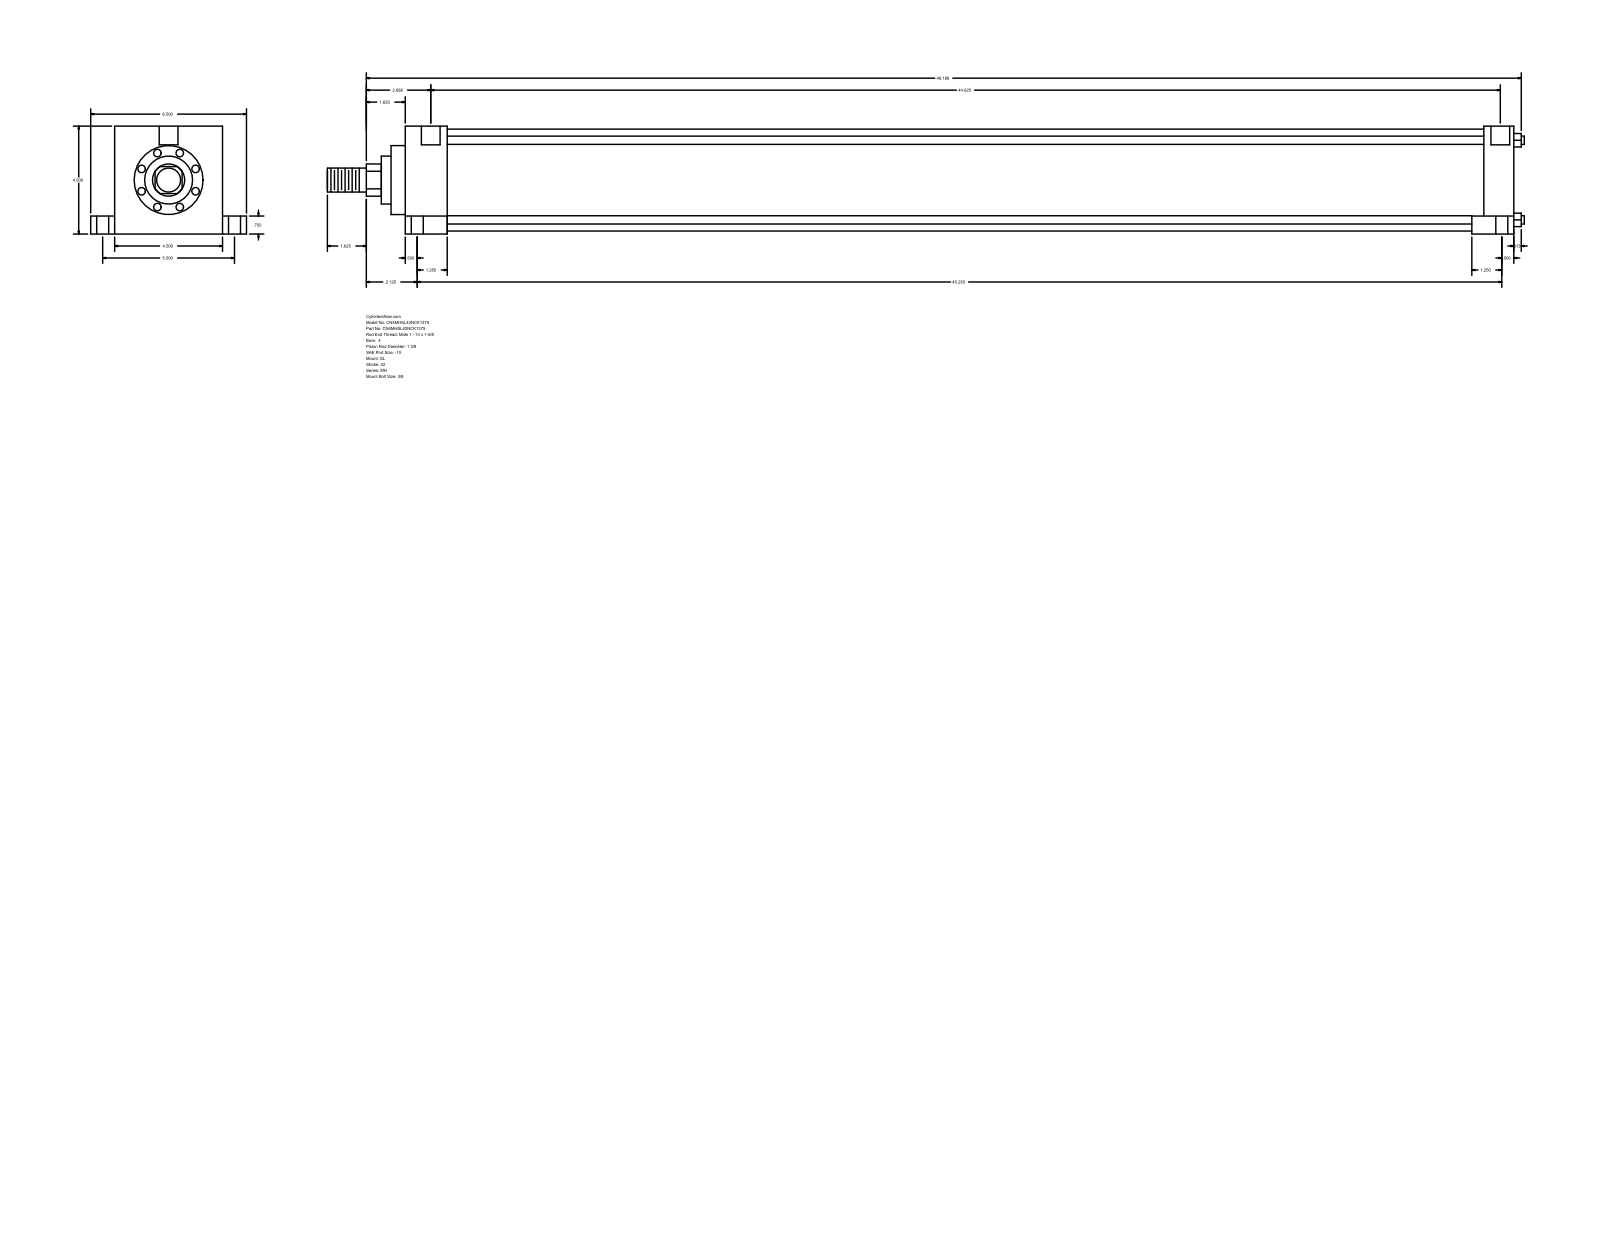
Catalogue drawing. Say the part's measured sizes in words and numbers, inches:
The part is named "MH_SL__0400_1.375". Its 3-D file was written by "GSSL Pune (CONFIG_CONTROL_DESIGN)". It is 0 solids with 110 faces: 77 planar, 33 cylindrical and 0 other. Overall it measures 49.937 by 6.5 by 4.5 inches. Round holes: 4 of diameter 0.344, 4 of diameter 0.5, 4 of diameter 0.75, 2 of diameter 0.781. Round bosses or shafts: 4 of diameter 0.345, 1 of diameter 4.25, 1 of diameter 2.875, 1 of diameter 2, 1 of diameter 1.375, 1 of diameter 1. Partial cylindrical surfaces (rounded edges, fillets, slot ends): 1 of radius 0.672. The main face-to-face distances are 4.5, 46.25, 1.75, 44.5, 45, 43.25, 1.25, 1, 5.5, 0.75. The hole center spacings are 0.063, 2.75, 2.751, 2.795, 2.807, 5.5, 44.688, 44.75.
